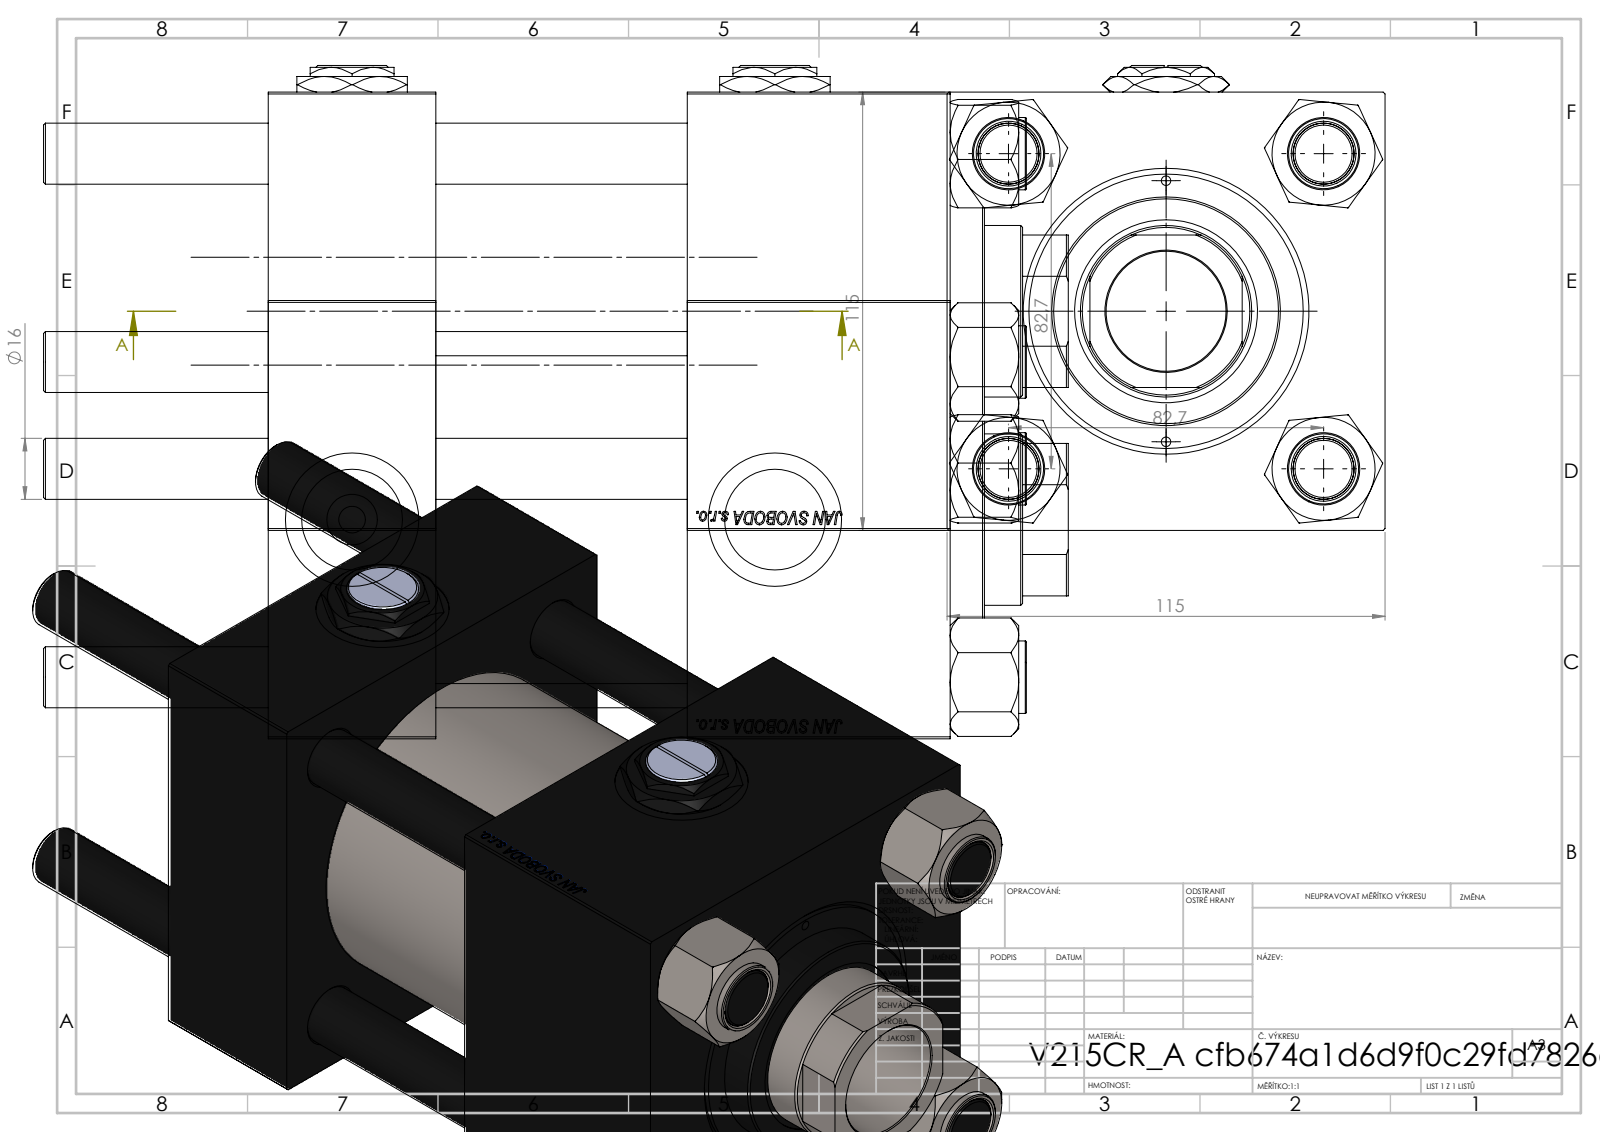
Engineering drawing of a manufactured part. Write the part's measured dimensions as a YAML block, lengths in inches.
part_name: "V215CR_VCP; CR025_012_A_0_G_A_G_M_020_+#_##_TYCINKA; V215_VC_A; V215CR_BODY_A (+2 more)"
step_written_by: "SolidWorks 2019 (CONFIG_CONTROL_DESIGN)"
units: inches
bodies: {solids: 13, faces: 1287, planar: 617, cylindrical: 92, other: 578}
overall_size: [10.591, 4.803, 4.528]
volume: 115
surface_area: 475.9
round_holes:
  - {diameter: 0.63, count: 4}
  - {diameter: 0.098, count: 2}
  - {diameter: 0.276, count: 2}
  - {diameter: 1.041, count: 2}
  - {diameter: 1.378, count: 2}
  - {diameter: 1.24, count: 1}
  - {diameter: 1.772, count: 1}
  - {diameter: 1.89, count: 1}
  - {diameter: 2.402, count: 1}
  - {diameter: 2.835, count: 1}
  - {diameter: 3.15, count: 1}
round_bosses_or_shafts:
  - {diameter: 0.748, count: 4}
  - {diameter: 3.386, count: 1}
  - {diameter: 2.362, count: 1}
partial_cylinders:
  - {radius: 0.866, count: 1}
face_to_face_distances: [4.528, 1.732, 7.047, 5.315, 4.331, 2.717, 2.598, 0.787, 3.504, 5.917]
hole_center_spacings: [1.652, 2.302, 3.256, 3.393, 1.348, 4.605, 2.697, 4.37]
